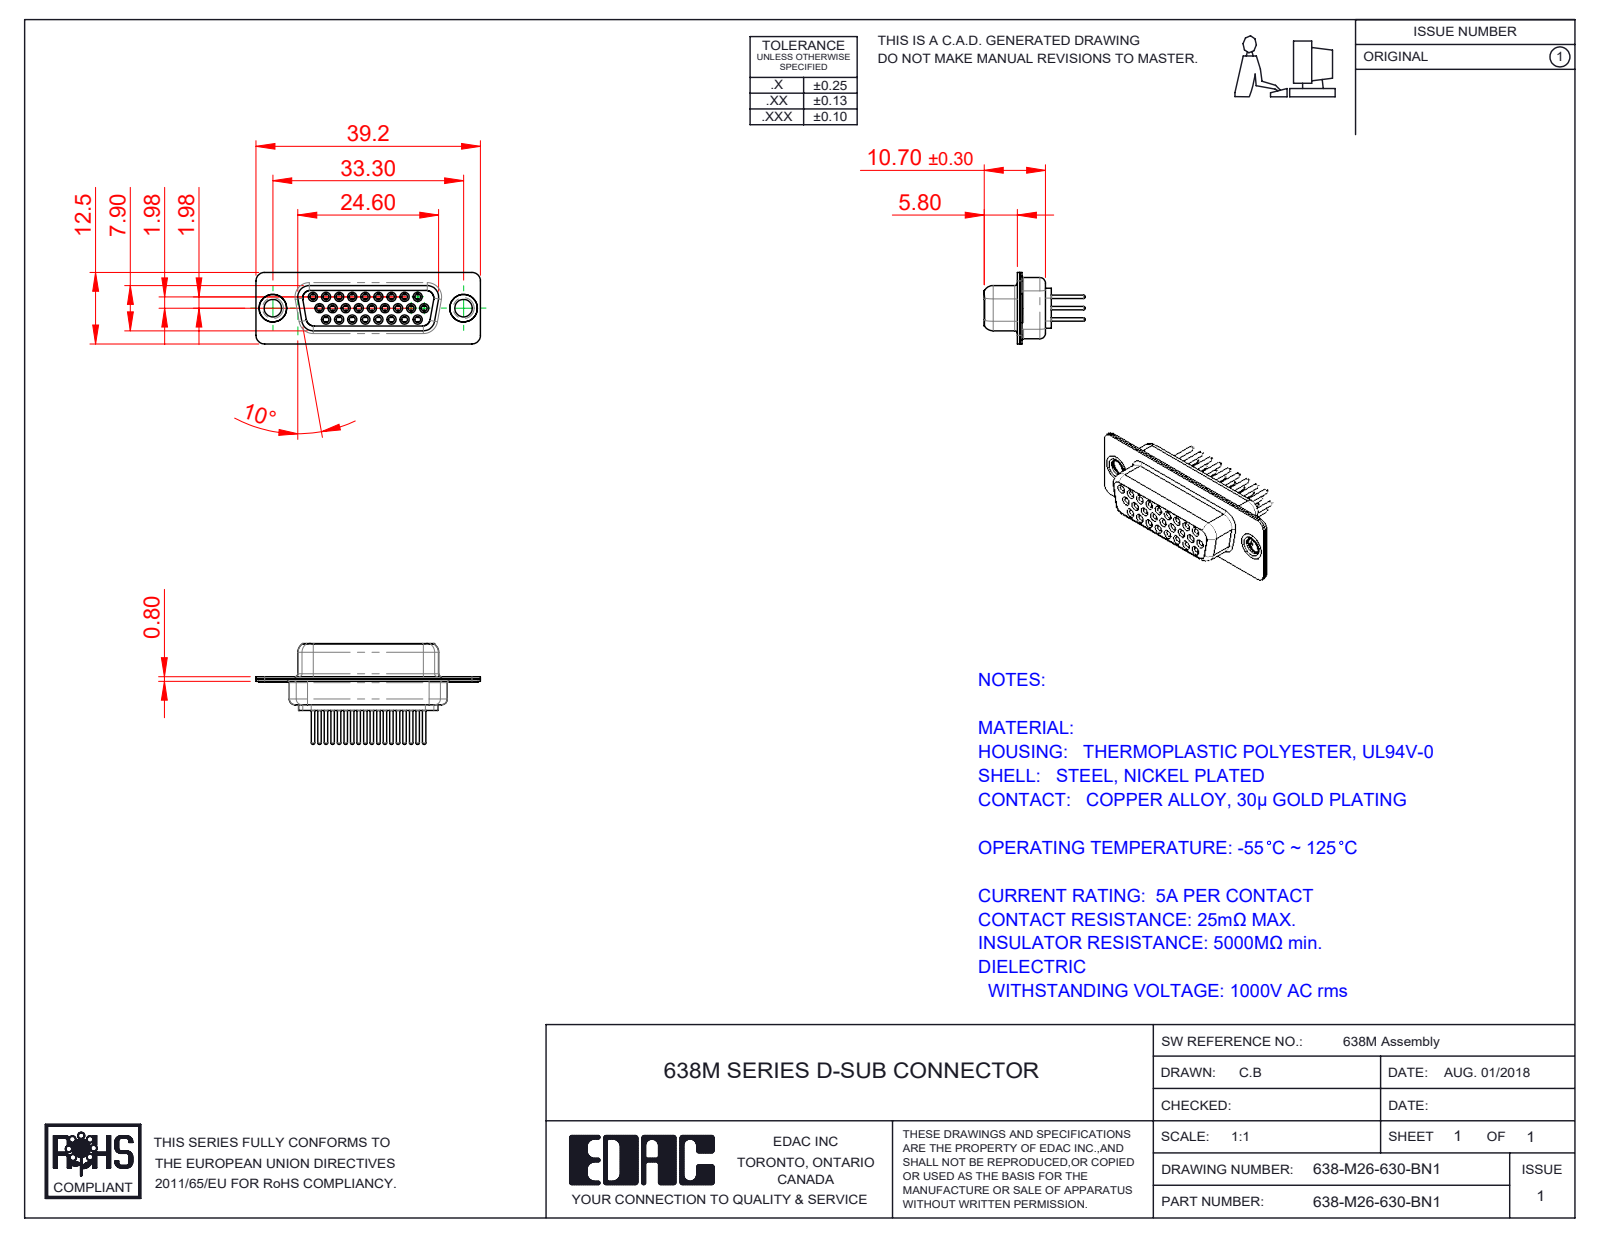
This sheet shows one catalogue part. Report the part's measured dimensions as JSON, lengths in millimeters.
{"part_name": "638M Housing_26 Contacts; 638M Shell Rear_26 Contacts; 638M Contact Row 1_30; 638M Contact Row 3_30 (+4 more)", "step_written_by": "SolidWorks 2020 (CONFIG_CONTROL_DESIGN)", "units": "millimeters", "bodies": {"solids": 31, "faces": 1683, "planar": 457, "cylindrical": 615, "other": 611}, "overall_size": [39.2, 17.6, 12.5], "volume_mm3": 2275, "surface_area_mm2": 7716, "round_holes": [[1, 26], [1.1, 26], [1.7, 26], [1.8, 26], [2, 26], [3.05, 2], [4, 2], [4.8, 2]], "round_bosses_or_shafts": [[2.2, 26], [1.6, 26], [1.5, 26], [0.6, 26], [5, 2], [4.9, 2], [3.55, 2]], "partial_cylinders_radius": [[1.5, 16], [2, 12], [1.35, 8], [1.6, 8], [0.25, 4], [0.5, 4], [0.6, 4], [0.65, 4]], "face_to_face_distances": [0.4, 1.4, 0.45, 8.45, 8.9, 1.8, 1, 6.2, 7.05, 1.35], "hole_center_spacings": [3.96, 2.28, 4.57, 6.05, 2.29, 8.24, 6.86, 6.04]}
